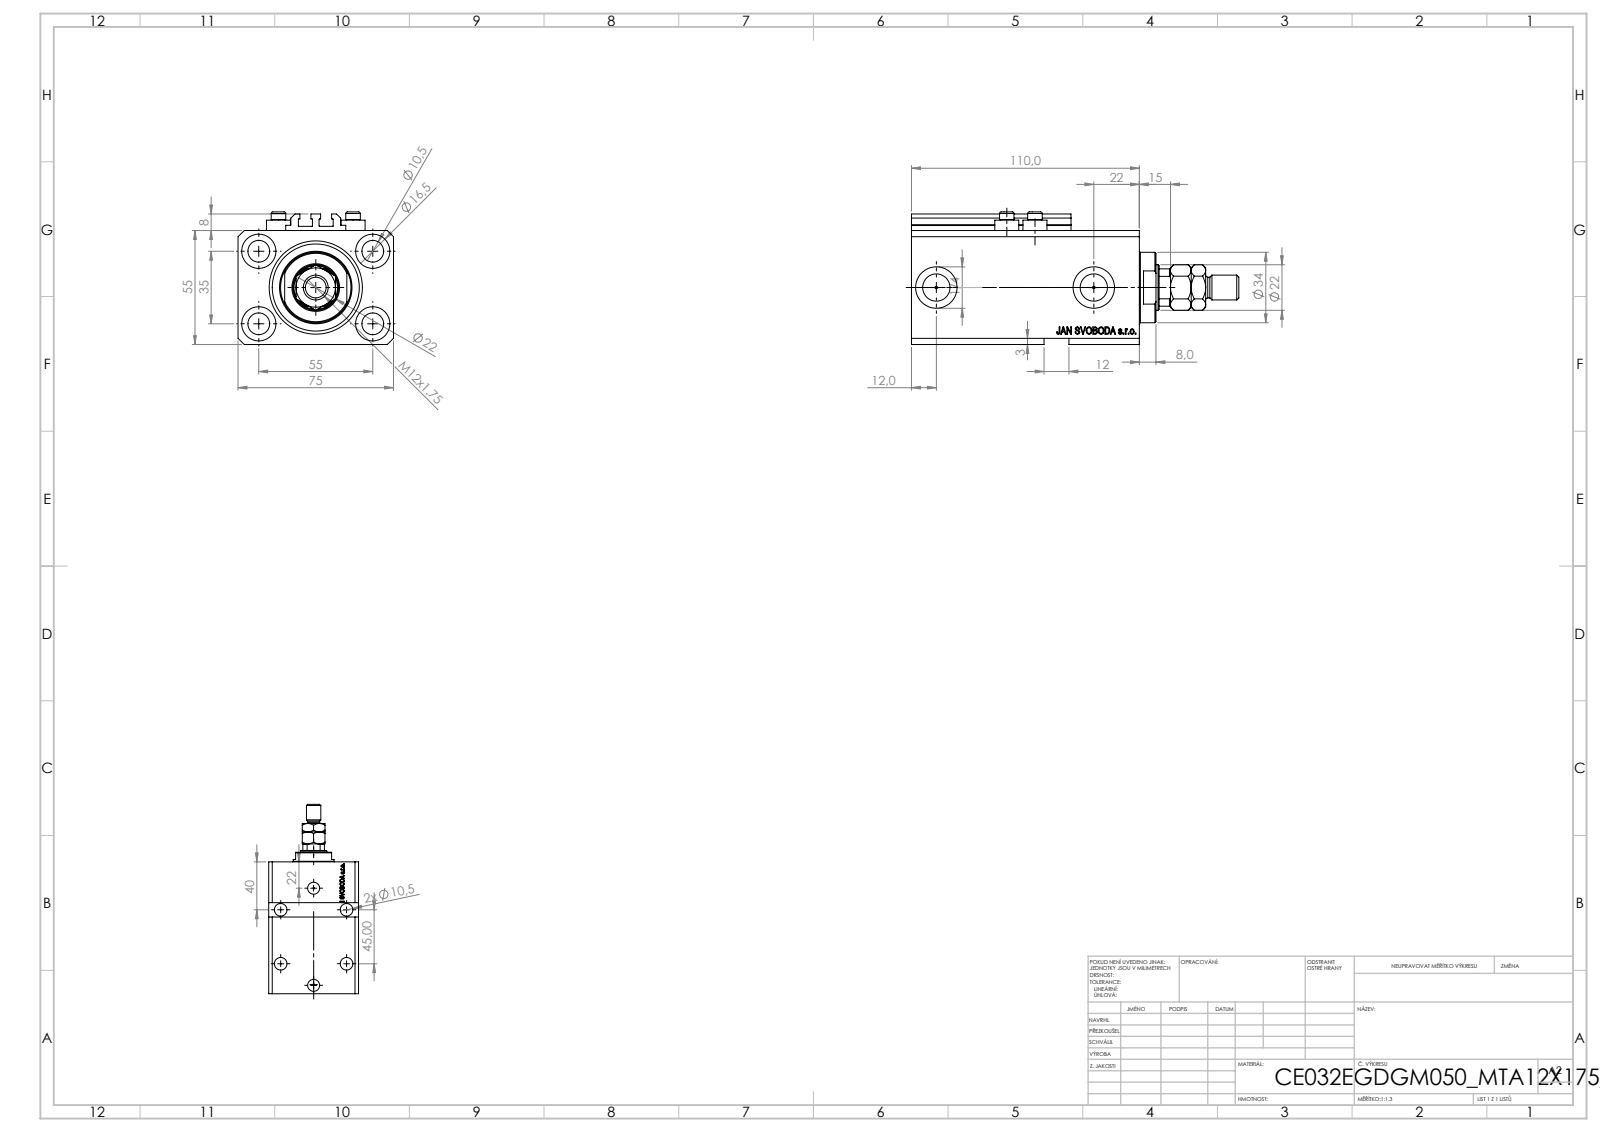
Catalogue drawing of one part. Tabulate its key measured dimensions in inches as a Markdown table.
| quantity | value |
| --- | --- |
| part name | V250CE_C_VCP; V250CE_E_Body; MTA; V250CE_VC_E (+1 more) |
| STEP written by | SolidWorks 2019 (CONFIG_CONTROL_DESIGN) |
| units | inches |
| bodies | 9 solids, 1149 faces (533 planar, 162 cylindrical, 454 other) |
| overall size | 6.22 × 2.953 × 2.52 |
| volume | 23.48 in³ |
| surface area | 153.6 in² |
| round holes (diameter × count) | 0.413 × 9, 0.049 × 4, 0.157 × 4, 0.65 × 4, 0.394 × 2, 0.518 × 2, 0.787 × 2, 0.866 × 1, 1.26 × 1, 1.772 × 1 |
| round bosses / shafts (diameter × count) | 0.457 × 4, 0.276 × 4, 1.339 × 1, 0.472 × 1, 0.394 × 1 |
| partial cylindrical surfaces (radius × count) | 0.008 × 10, 0.413 × 1 |
| main face-to-face distances | 2.165, 2.953, 0.591, 4.331, 3.74, 0.39, 0.118, 3.35, 3.941, 0.098 |
| hole center spacings | 1.283, 1.294, 2.165, 2.706, 0.535, 0.555, 0.907, 1.016 |
